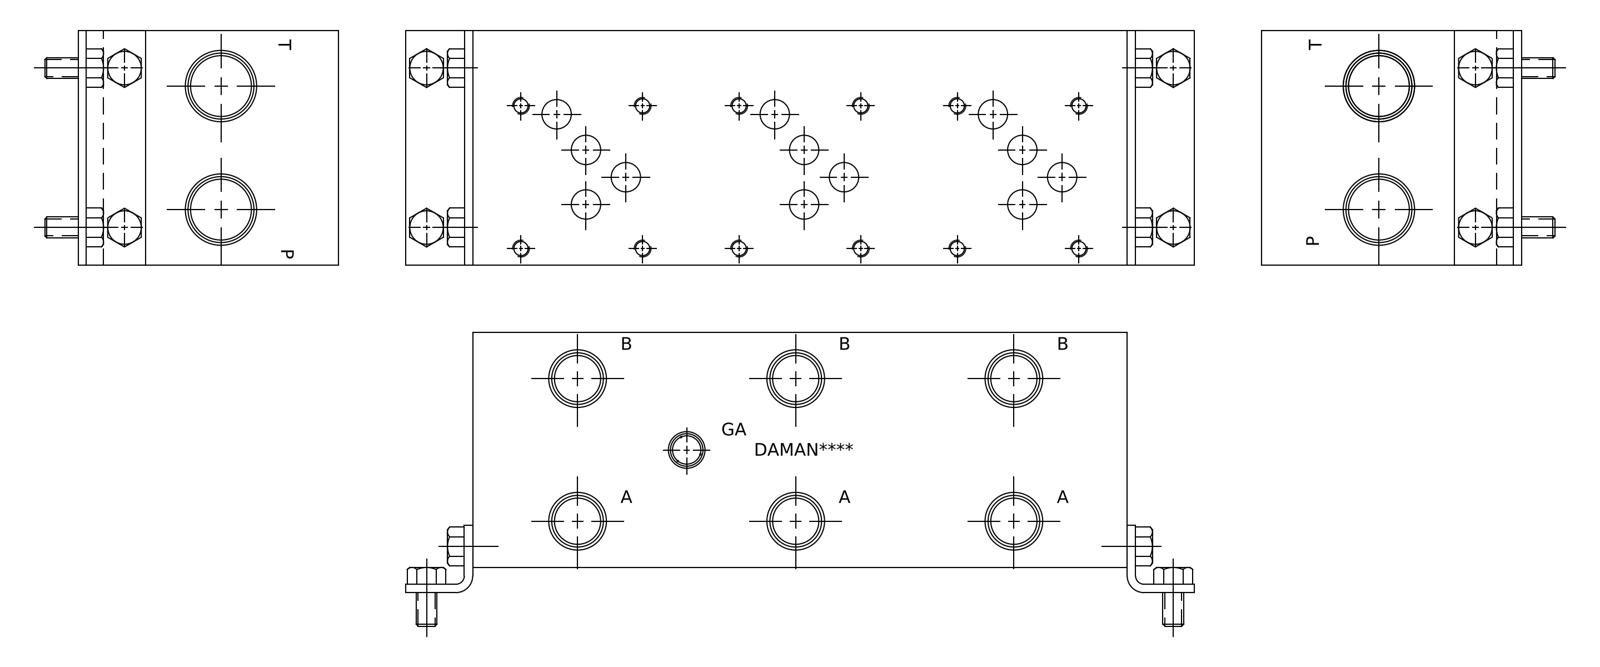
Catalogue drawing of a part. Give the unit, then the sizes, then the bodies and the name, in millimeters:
Units: millimetres
Overall size (bounding box): 247.65 × 88.9 × 88.9
Round holes (diameter × count): ⌀5.11 ×12, ⌀6.35 ×12, ⌀11.13 ×11, ⌀17.48 ×6, ⌀21.59 ×6, ⌀6.53 ×2, ⌀7.92 ×2, ⌀23.01 ×2, ⌀26.92 ×2, ⌀10.72 ×1, ⌀11.11 ×1, ⌀13.87 ×1
Main face-to-face distances: 88.9, 247.65, 15.37, 73.53, 15.85, 231.8, 215.95, 1, 14.37, 87.9
Hole centre spacings: 82.55, 165.1, 98.63, 46.05, 70.95, 53.98, 36.5, 98.61
Volume: 1 861 000 mm³ · Surface area: 126 049 mm²
Bodies: 1 solid, 666 faces (382 planar, 66 cylindrical, 218 other)
Part name (STEP PRODUCT): Part_AD05P033P_3D
STEP written by: Autodesk Inventor 2019 (AUTOMOTIVE_DESIGN)
